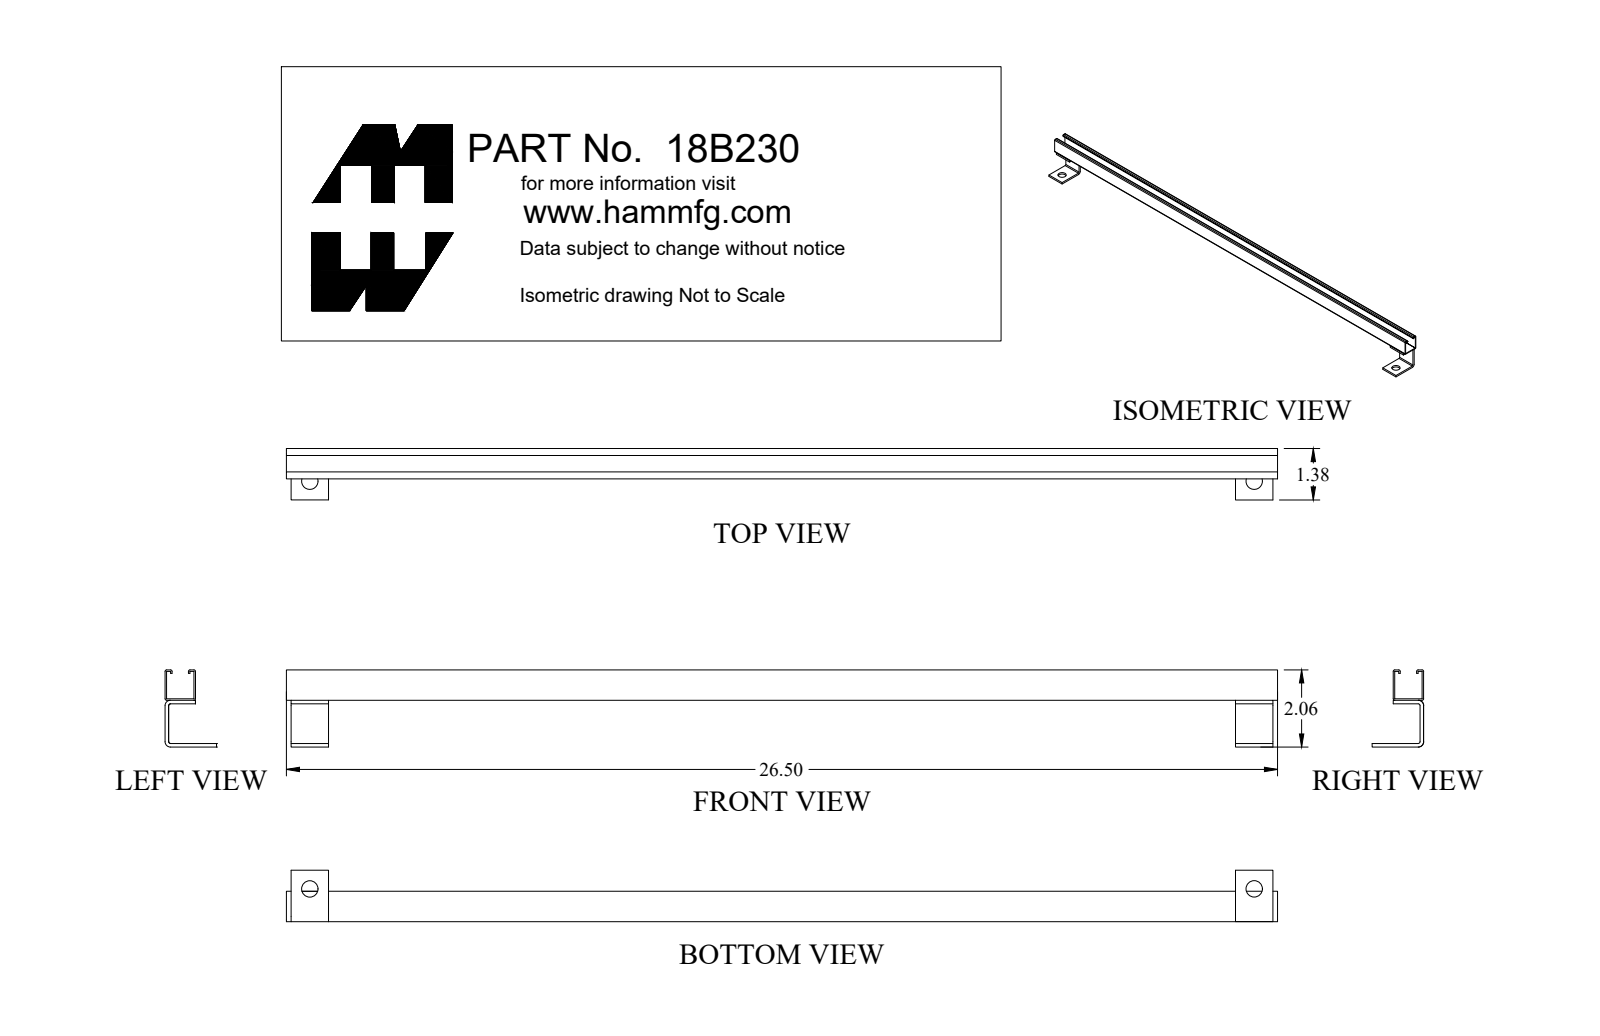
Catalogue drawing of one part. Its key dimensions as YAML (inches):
part_name: "18B230"
step_written_by: "SolidWorks 2018 (AUTOMOTIVE_DESIGN)"
units: inches
bodies: {solids: 3, faces: 60, planar: 38, cylindrical: 22, other: 0}
overall_size: [26.5, 2.063, 1.376]
volume: 3.439
surface_area: 159.5
round_holes:
  - {diameter: 0.437, count: 2}
partial_cylinders:
  - {radius: 0.043, count: 6}
  - {radius: 0.048, count: 4}
  - {radius: 0.143, count: 4}
face_to_face_distances: [0.04, 0.773, 0.813, 0.733, 0.773, 0.813, 0.733, 0.625, 0.148, 0.095]
hole_center_spacings: [11.25]
